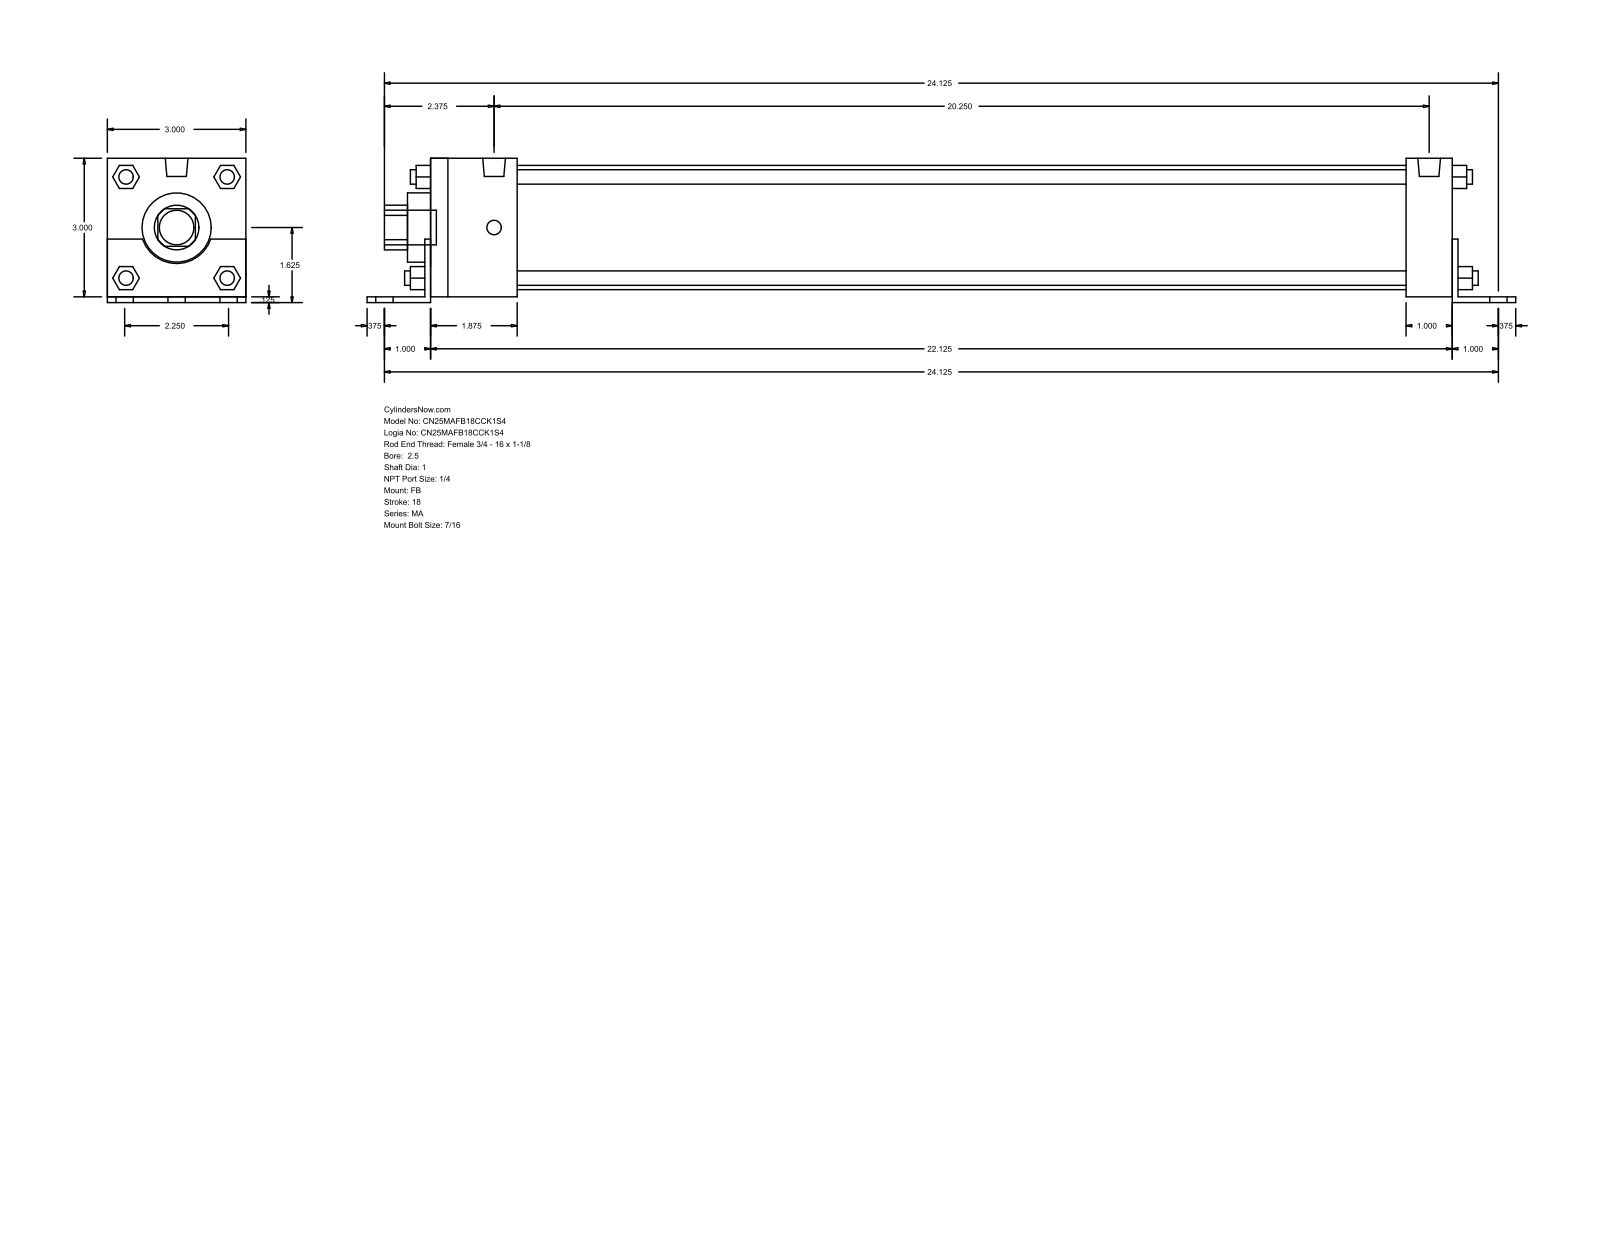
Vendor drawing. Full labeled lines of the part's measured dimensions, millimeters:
Part name (STEP PRODUCT): MA_FB__0250_1
STEP written by: GSSL Pune (CONFIG_CONTROL_DESIGN)
Units: millimetres
Bodies: 0 solids, 140 faces (105 planar, 35 cylindrical, 0 other)
Overall size (bounding box): 631.83 × 79.38 × 76.2
Round holes (diameter × count): ⌀25.4 ×1, ⌀38.1 ×1, ⌀68.33 ×1
Round bosses / shafts (diameter × count): ⌀7.94 ×8, ⌀11.11 ×6, ⌀12.49 ×2, ⌀19.05 ×1
Partial cylindrical surfaces — rounded edges, fillets, slot ends (radius × count): R12.29 ×1, R19.81 ×1
Main face-to-face distances: 76.2, 3.17, 79.37, 565.15, 561.98, 12.7, 25.4, 28.57, 47.63, 514.35
